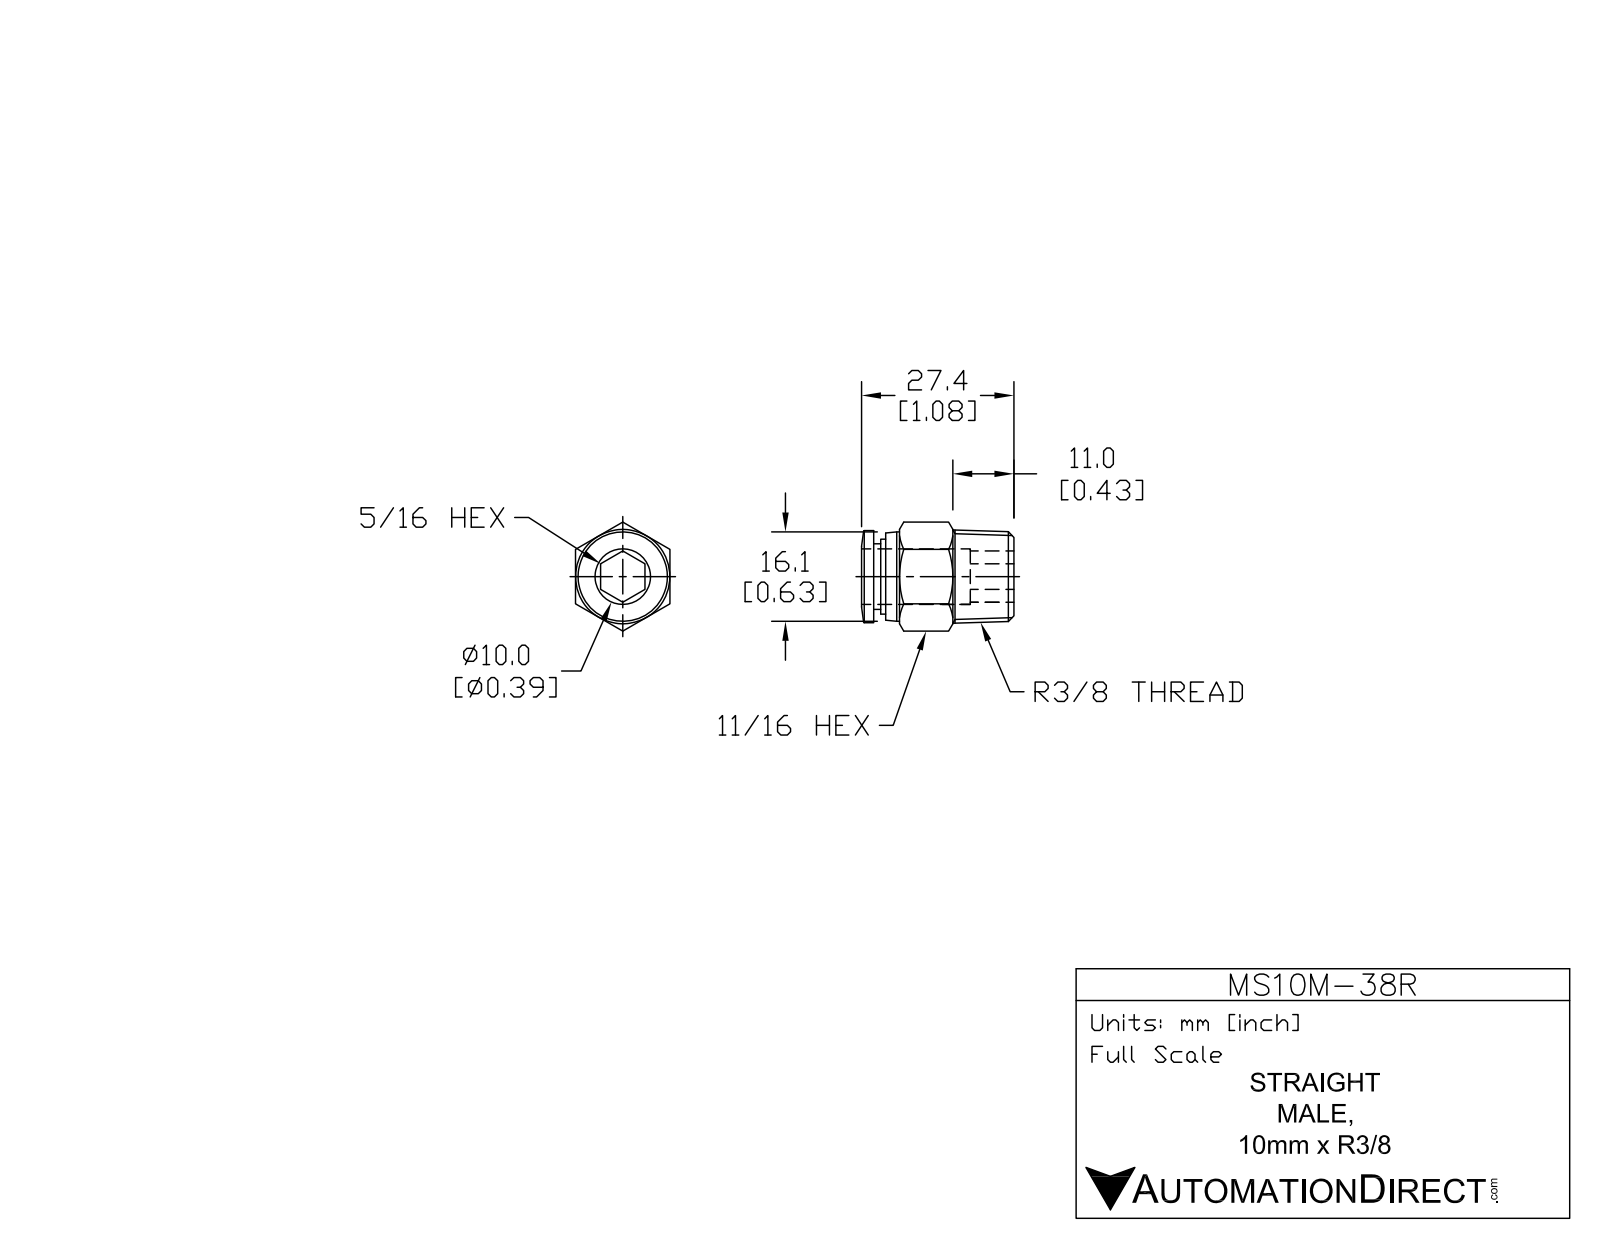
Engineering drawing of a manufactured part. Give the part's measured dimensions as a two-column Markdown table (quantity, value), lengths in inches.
| quantity | value |
| --- | --- |
| part name | MS10M-38R |
| STEP written by | SolidWorks 2015 (AUTOMOTIVE_DESIGN) |
| units | inches |
| bodies | 1 solid, 52 faces (14 planar, 12 cylindrical, 26 other) |
| overall size | 1.081 × 0.773 × 0.669 |
| volume | 0.238 in³ |
| surface area | 4.338 in² |
| round holes (diameter × count) | 0.315 × 1, 0.406 × 1 |
| round bosses / shafts (diameter × count) | 0.654 × 1, 0.634 × 1, 0.531 × 1, 0.465 × 1 |
| main face-to-face distances | 0.669, 0.994, 0.909, 0.085, 0.945, 0.035, 0.049, 0.309, 0.6, 0.636 |
